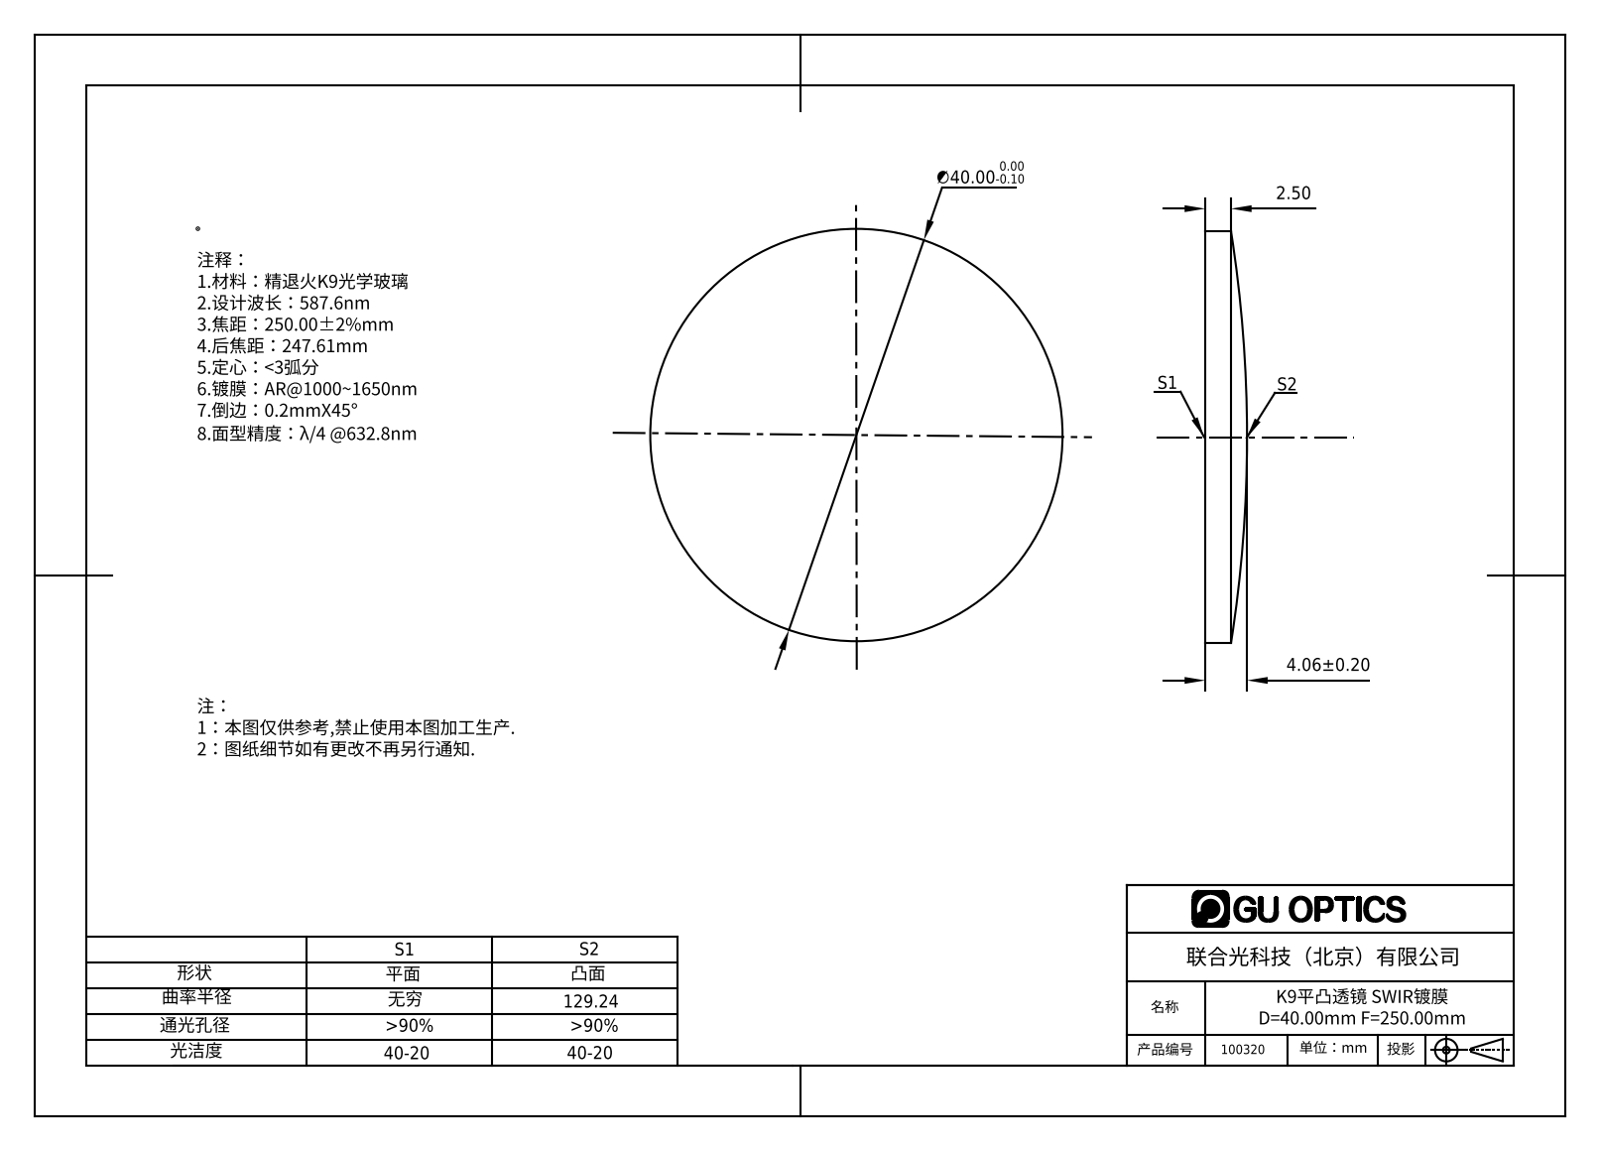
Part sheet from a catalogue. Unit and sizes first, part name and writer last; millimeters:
Units: millimetres
Overall size (bounding box): 40 × 40 × 4.06
Round bosses / shafts (diameter × count): ⌀40 ×1
Volume: 4 124 mm³ · Surface area: 2 835 mm²
Bodies: 1 solid, 5 faces (1 planar, 2 cylindrical, 2 other)
Part name (STEP PRODUCT): 100148
STEP written by: SolidWorks 2016 (AUTOMOTIVE_DESIGN)
